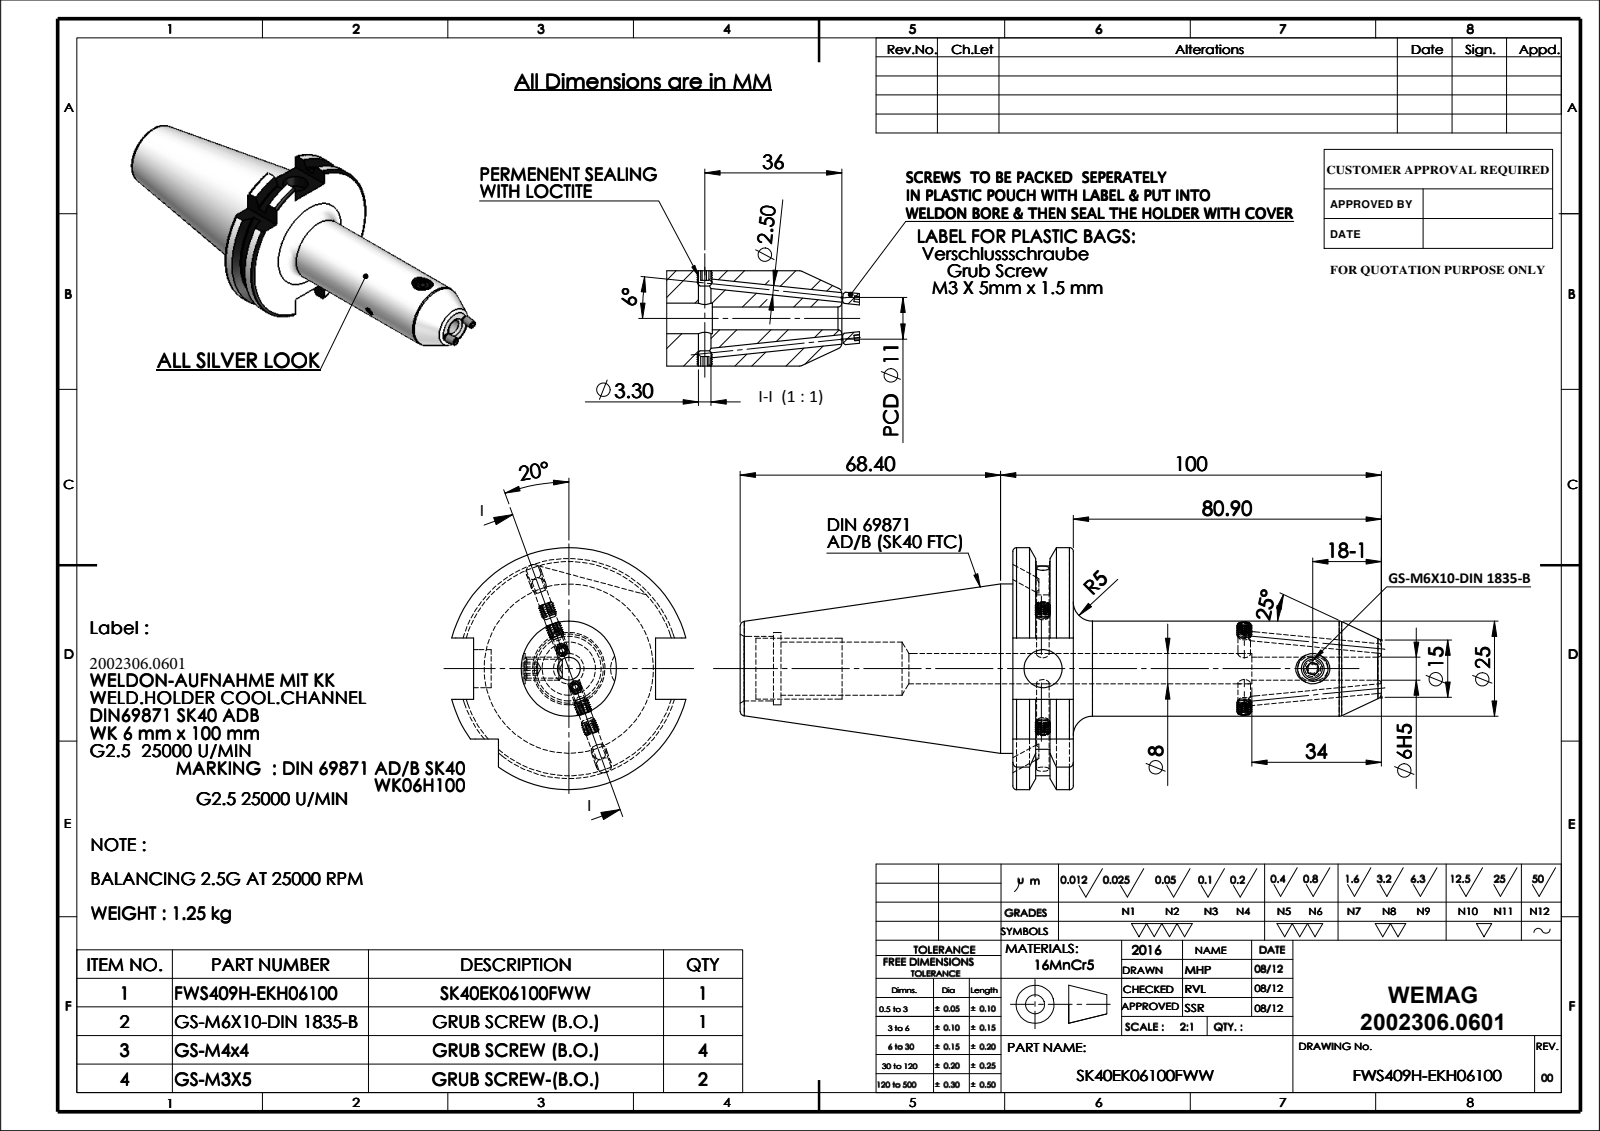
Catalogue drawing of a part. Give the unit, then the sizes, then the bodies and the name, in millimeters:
Units: millimetres
Overall size (bounding box): 173.78 × 63.55 × 61.48
Round holes (diameter × count): ⌀3.3 ×3, ⌀2.5 ×2, ⌀8 ×2, ⌀5 ×1, ⌀6 ×1, ⌀10 ×1, ⌀14 ×1, ⌀17 ×1, ⌀19 ×1
Round bosses / shafts (diameter × count): ⌀4 ×4, ⌀3 ×2, ⌀44.45 ×1, ⌀25 ×1, ⌀6 ×1
Partial cylindrical surfaces — rounded edges, fillets, slot ends (radius × count): R28.12 ×1, R31.77 ×1
Main face-to-face distances: 15.9, 16.1, 47.8, 71.6, 87.5, 10.7, 60.9, 76.8, 77.63, 66.93
Hole centre spacings: 52.9, 1.13, 70.85
Volume: 137 536 mm³ · Surface area: 29 887 mm²
Bodies: 8 solids, 360 faces (98 planar, 90 cylindrical, 172 other)
Part name (STEP PRODUCT): SK40EK06100FWW; GS-M6X10-DIN1835-B; 91406-WK206100; GS-M3X5_DIN 913 - M3 x 5-N (+1 more)
STEP written by: SolidWorks 2009 (CONFIG_CONTROL_DESIGN)
